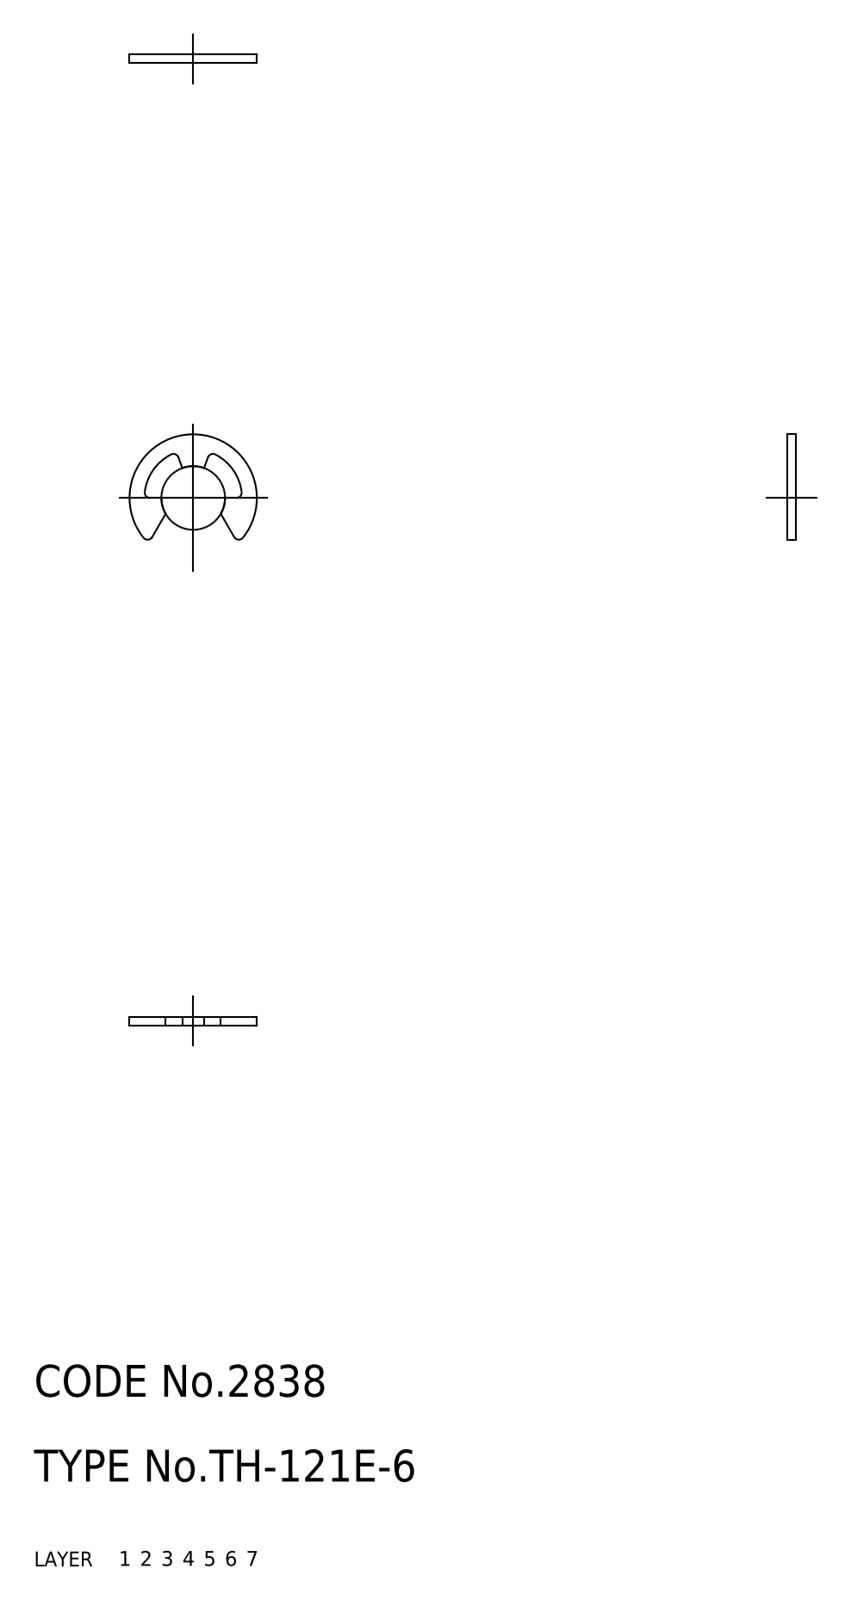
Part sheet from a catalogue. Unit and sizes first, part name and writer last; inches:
Units: inches
Overall size (bounding box): 0.472 × 0.391 × 0.031
Volume: 0.002 in³ · Surface area: 0.214 in²
Bodies: 1 solid, 20 faces (0 planar, 0 cylindrical, 20 other)
Part name (STEP PRODUCT): retainer
STEP written by: CADfix (AUTOMOTIVE_DESIGN)
